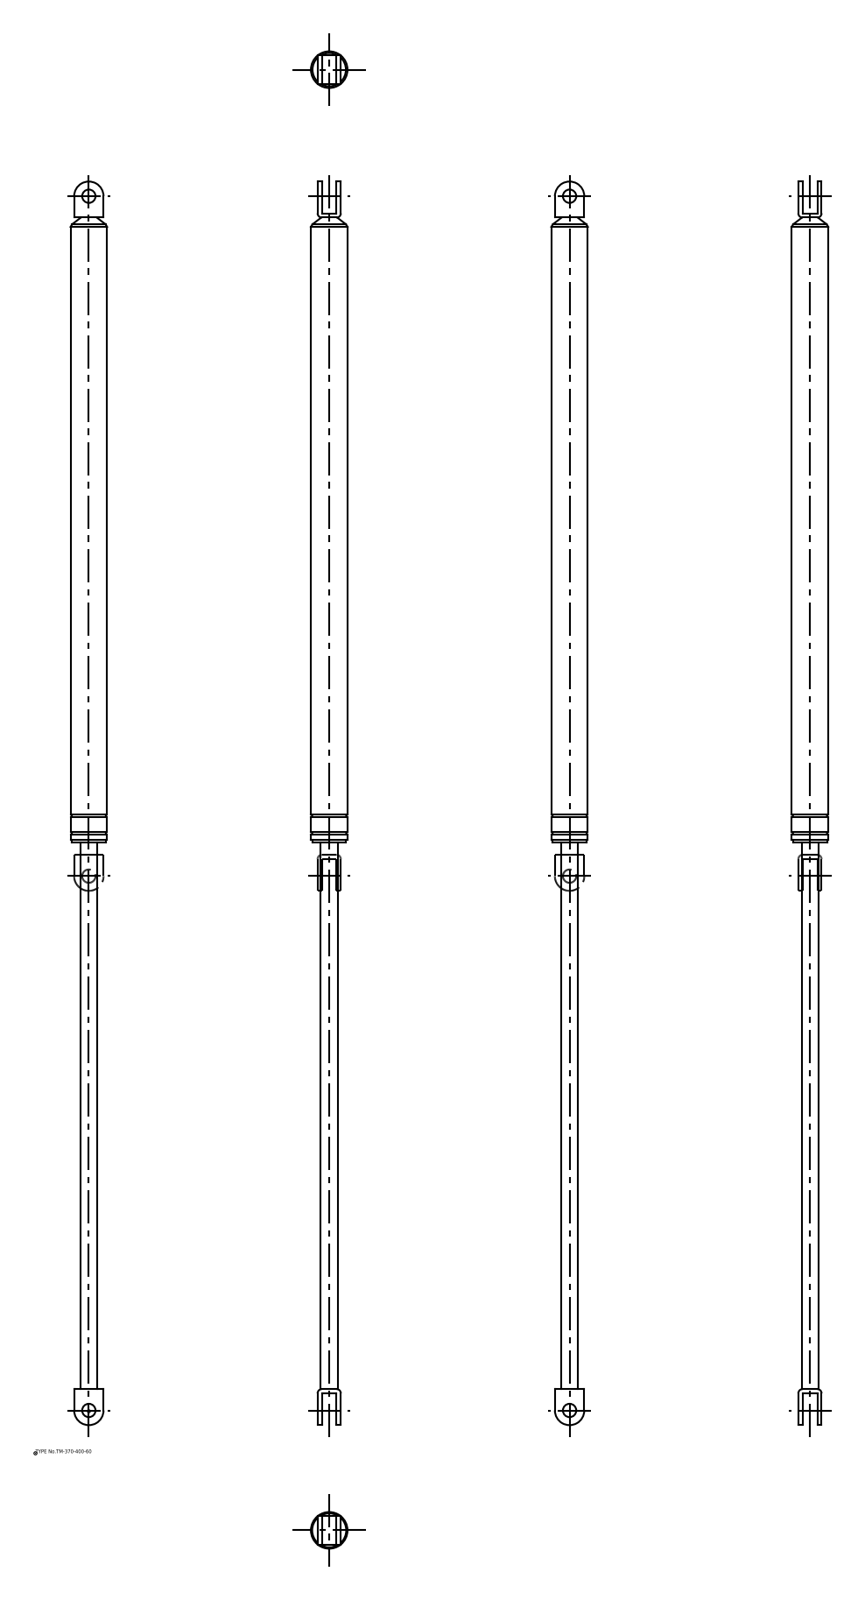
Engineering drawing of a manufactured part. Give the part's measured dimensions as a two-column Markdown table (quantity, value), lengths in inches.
| quantity | value |
| --- | --- |
| part name | TM_370_400_60; TM_370_400_60_div |
| STEP written by | spGate 16.7.1 (AUTOMOTIVE_DESIGN) |
| units | inches |
| bodies | 2 solids, 64 faces (22 planar, 32 cylindrical, 10 other) |
| overall size | 36.654 × 1.11 × 1.11 |
| volume | 20.25 in³ |
| surface area | 97.85 in² |
| round holes (diameter × count) | 0.394 × 2 |
| round bosses / shafts (diameter × count) | 1.11 × 1, 1.079 × 1, 1.004 × 1, 0.492 × 1 |
| partial cylindrical surfaces (radius × count) | 0.126 × 4, 0.433 × 2 |
| main face-to-face distances | 0.126, 0.559, 0.685, 0.433, 0.866, 34.654, 16.228, 34.78, 18.551, 18.425 |
| hole center spacings | 35.787 |
